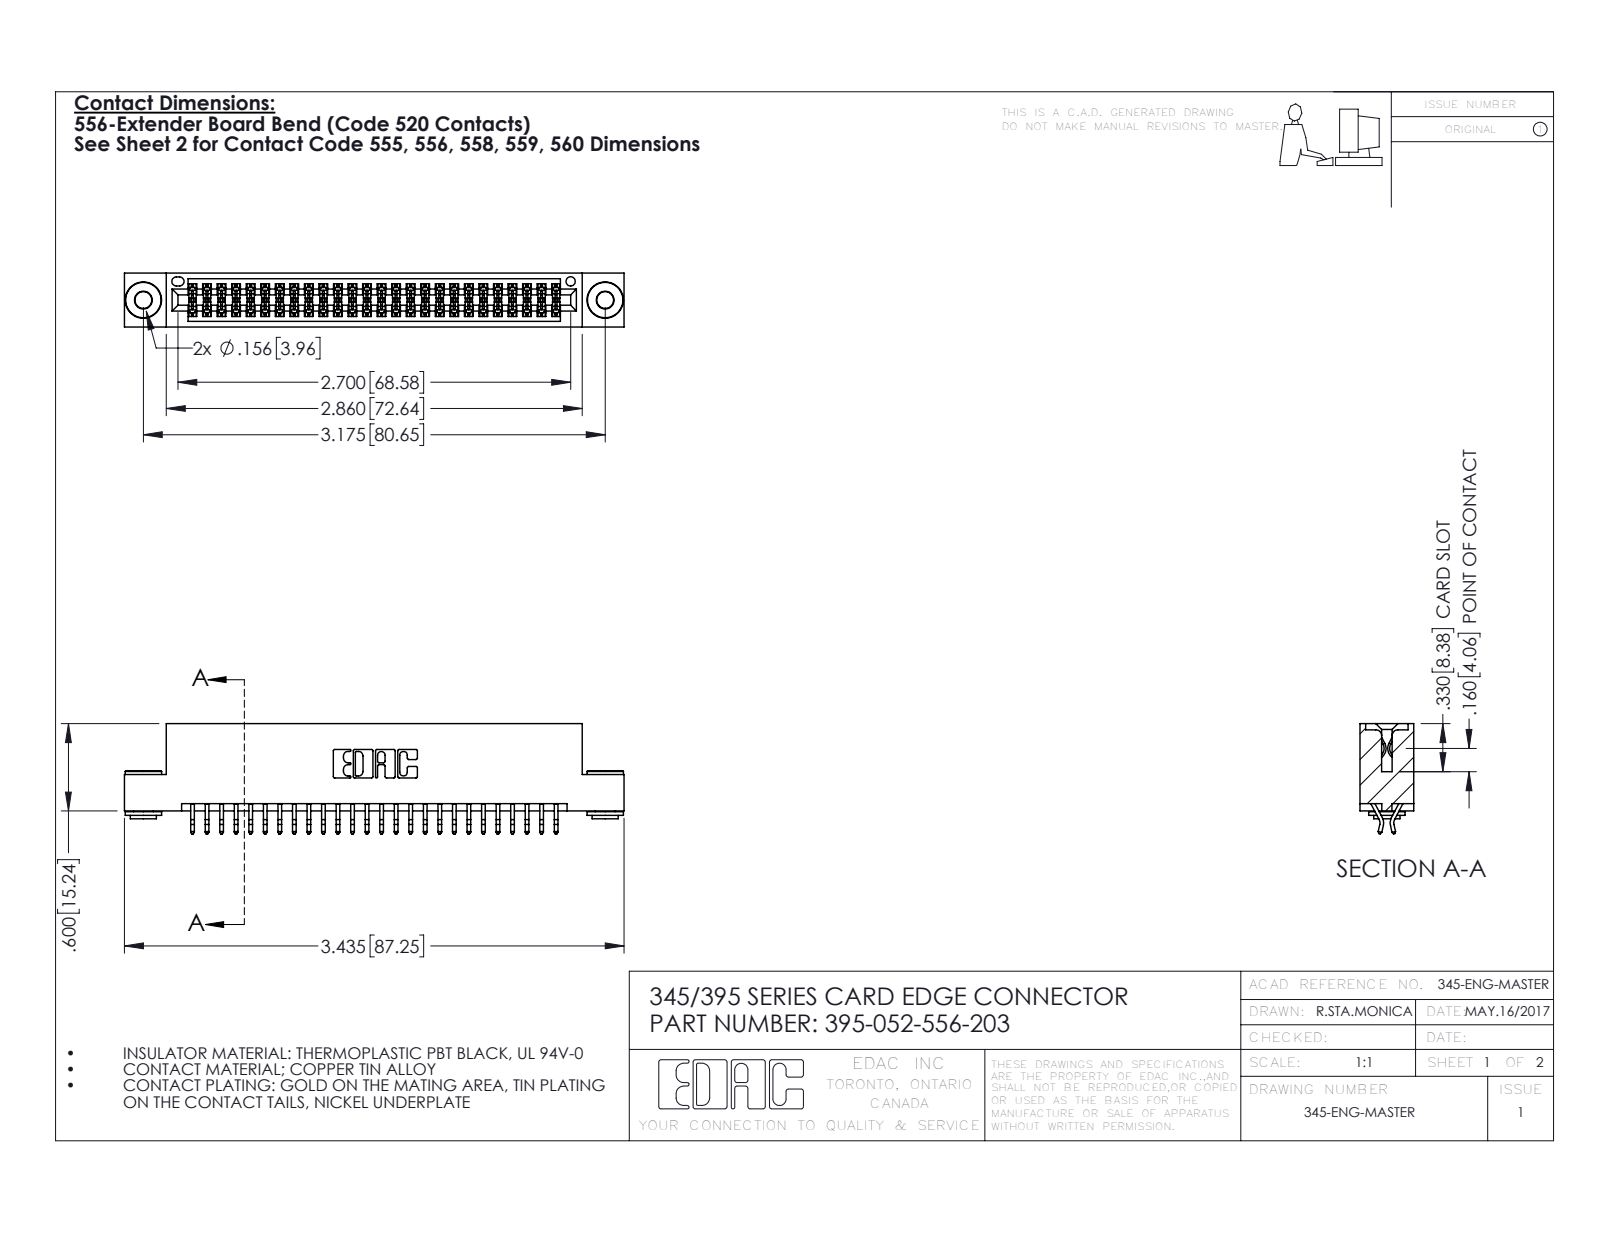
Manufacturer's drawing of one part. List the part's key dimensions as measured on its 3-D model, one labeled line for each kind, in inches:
Part name (STEP PRODUCT): 345-292-001_556 Tail; 395-052-556-203; 345-250-002_345-250-002-102; 345 Part_Flush Mounting Lugs - 0.156 Dia-TH
STEP written by: SolidWorks 2016 (CONFIG_CONTROL_DESIGN)
Units: inches
Bodies: 55 solids, 3076 faces (2014 planar, 1054 cylindrical, 8 other)
Overall size (bounding box): 3.435 × 0.757 × 0.37
Volume: 0.509 in³ · Surface area: 18.88 in²
Round holes (diameter × count): ⌀0.116 ×2, ⌀0.156 ×2, ⌀0.064 ×1
Round bosses / shafts (diameter × count): ⌀0.25 ×2, ⌀0.18 ×2, ⌀0.136 ×2
Partial cylindrical surfaces — rounded edges, fillets, slot ends (radius × count): R0.006 ×78, R0.01 ×22, R0.007 ×6, R0.031 ×6, R0.026 ×3, R0.01 ×2, R0.014 ×2, R0.019 ×2
Main face-to-face distances: 0.072, 0.298, 0.2, 0.37, 0.025, 0.098, 0.272, 0.225, 0.175, 0.149
Hole centre spacings: 0.27, 2.94, 3.175
